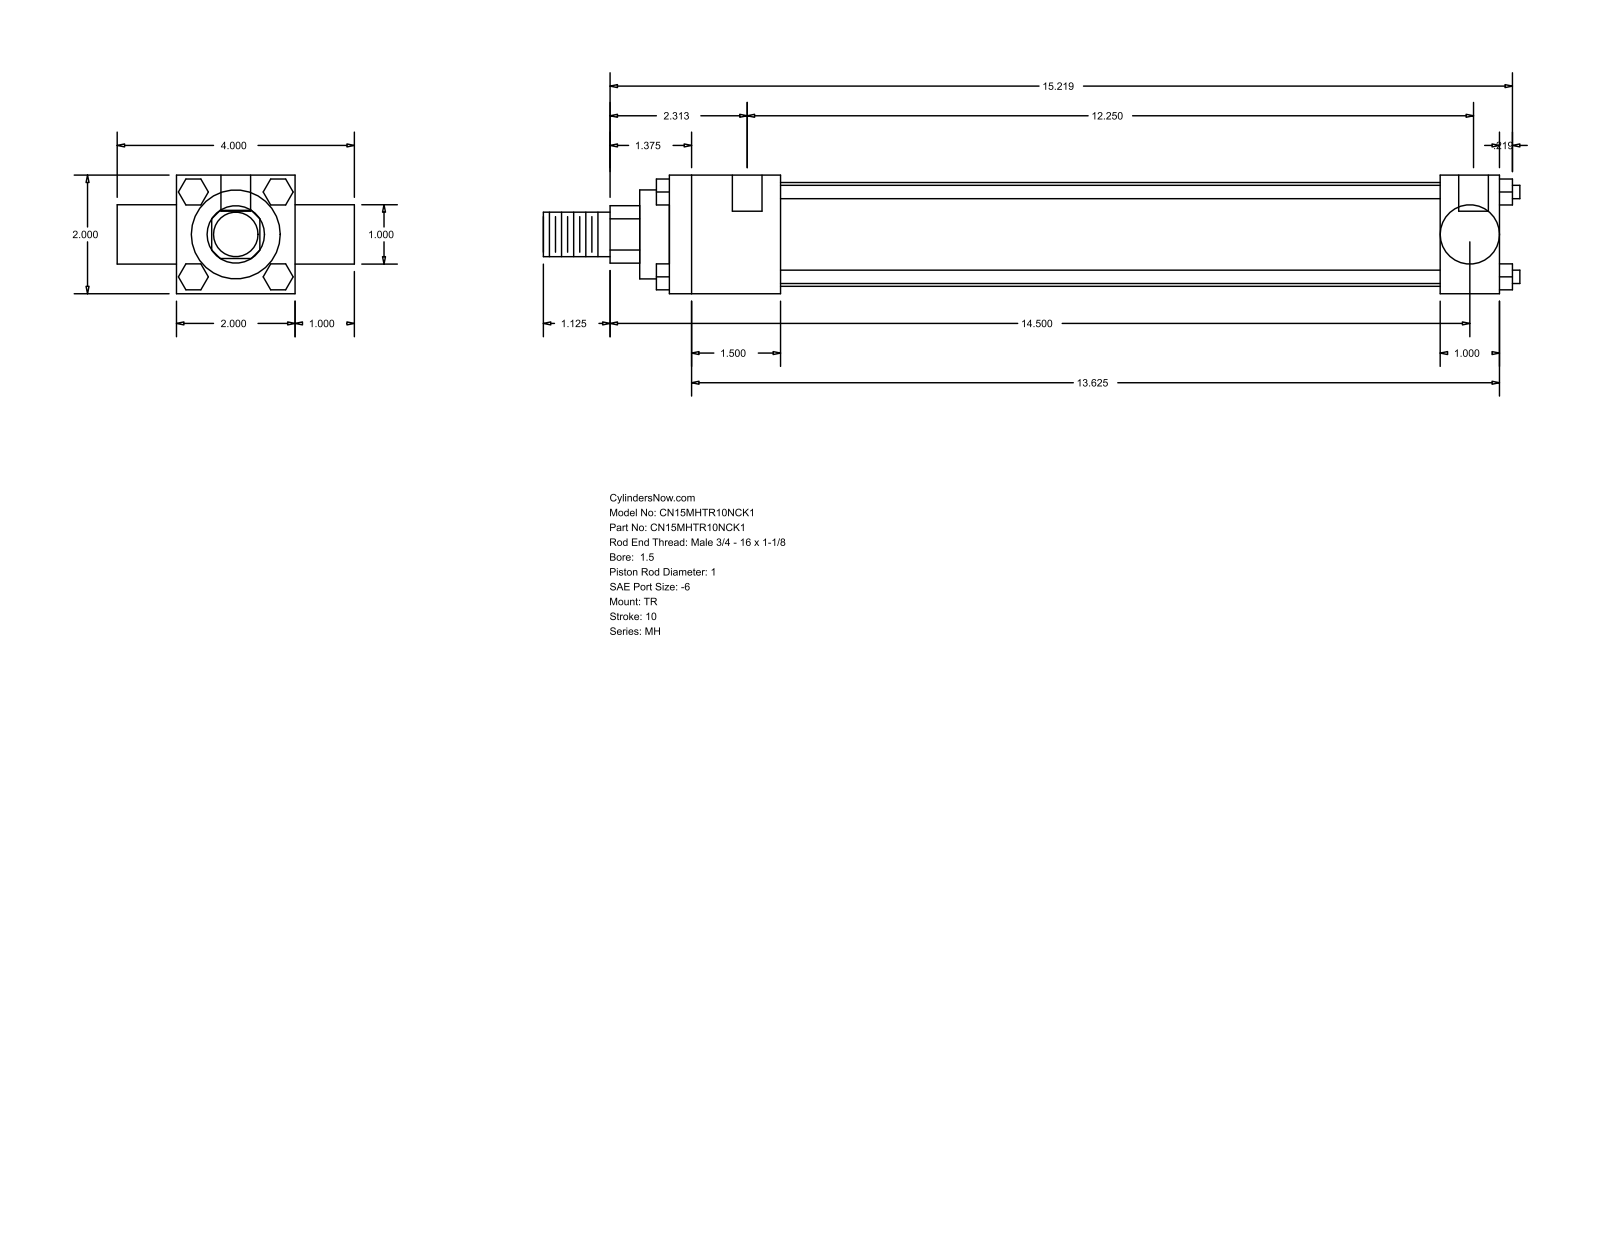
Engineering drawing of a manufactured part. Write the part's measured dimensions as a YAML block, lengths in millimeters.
part_name: "MH_TR__0150_1"
step_written_by: "GSSL Pune (CONFIG_CONTROL_DESIGN)"
units: millimeters
bodies: {solids: 0, faces: 120, planar: 92, cylindrical: 28, other: 0}
overall_size: [418.31, 101.6, 50.8]
round_holes:
  - {diameter: 5.56, count: 3}
  - {diameter: 12.7, count: 2}
round_bosses_or_shafts:
  - {diameter: 5.71, count: 4}
  - {diameter: 44.45, count: 1}
  - {diameter: 38.1, count: 1}
  - {diameter: 25.4, count: 1}
  - {diameter: 25.35, count: 1}
  - {diameter: 19.05, count: 1}
partial_cylinders:
  - {radius: 12.29, count: 1}
face_to_face_distances: [50.8, 25.4, 355.6, 76.2, 47.63, 307.97, 330.2, 282.57, 101.6, 12.7]
hole_center_spacings: [3.18, 311.15, 314.33]
